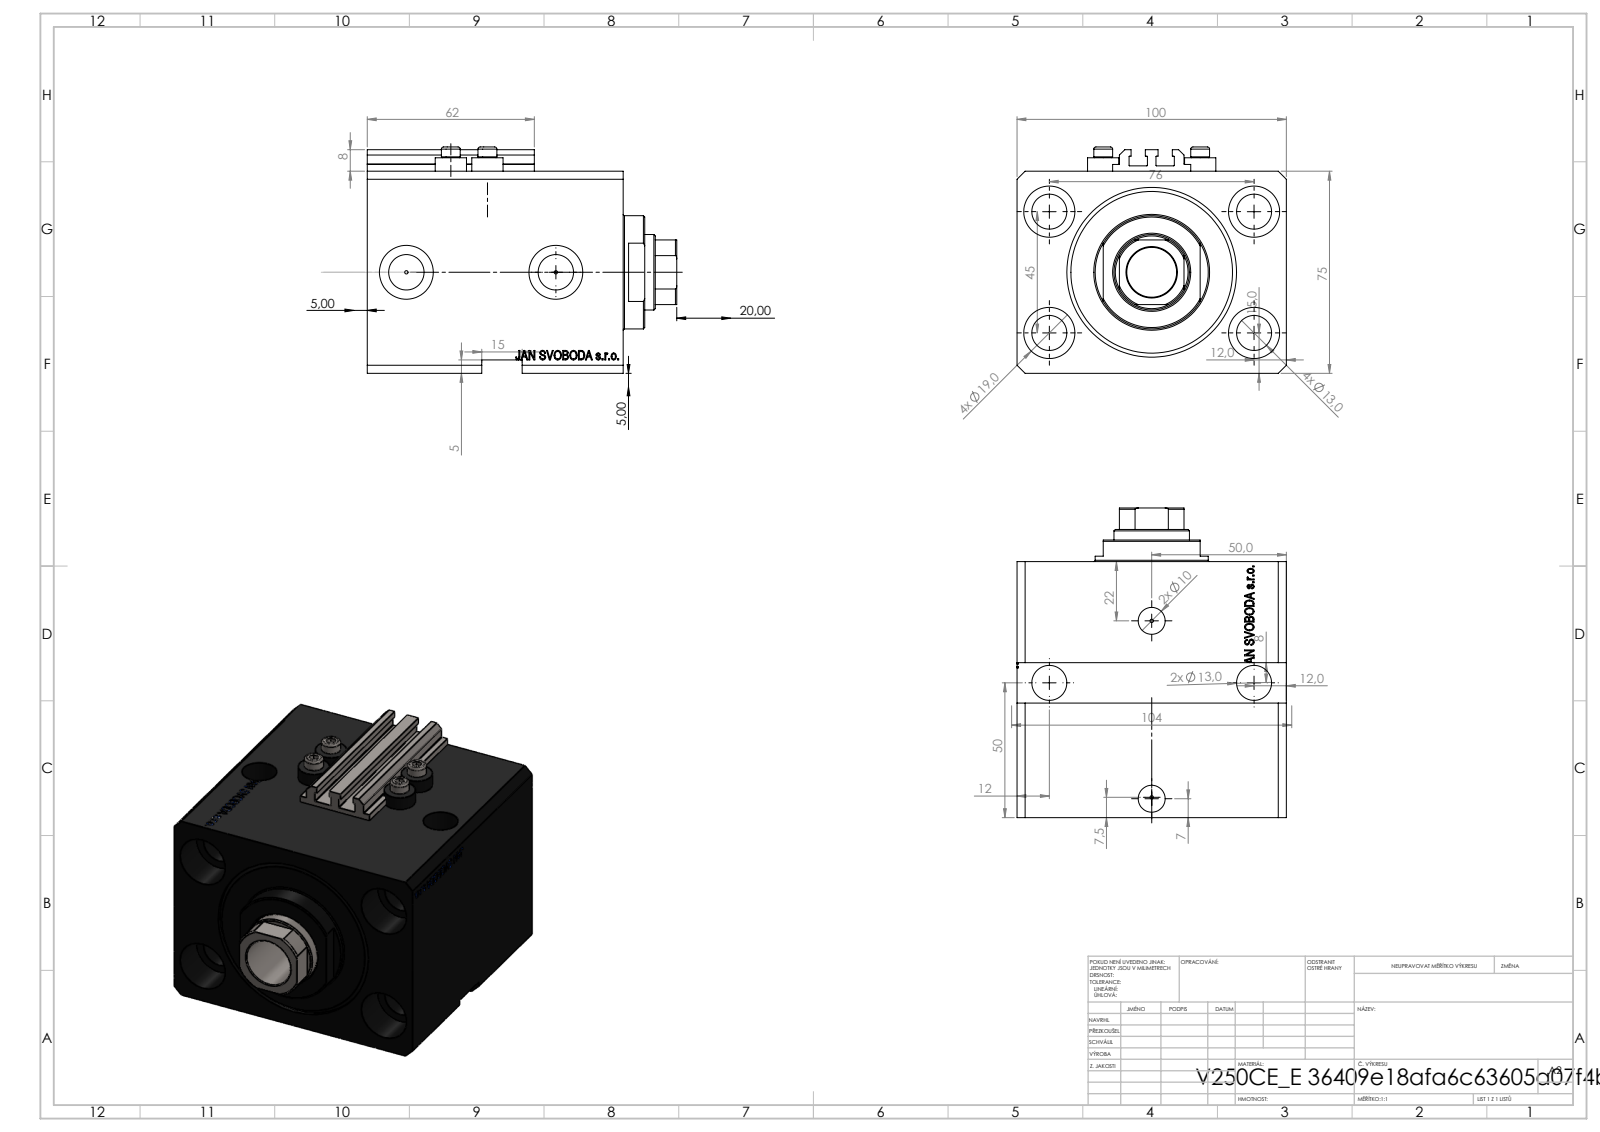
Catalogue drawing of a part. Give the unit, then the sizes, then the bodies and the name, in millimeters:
Units: millimetres
Overall size (bounding box): 114.9 × 100 × 84
Round holes (diameter × count): ⌀13 ×6, ⌀1.25 ×4, ⌀4 ×4, ⌀19 ×4, ⌀10 ×2, ⌀13.16 ×2, ⌀20 ×2, ⌀18.5 ×1, ⌀28 ×1, ⌀50 ×1, ⌀63 ×1
Round bosses / shafts (diameter × count): ⌀11.6 ×4, ⌀7 ×4, ⌀42 ×1
Partial cylindrical surfaces — rounded edges, fillets, slot ends (radius × count): R0.2 ×10, R13.5 ×1
Main face-to-face distances: 75, 100, 95, 11.9, 83.1, 68.4, 56.5, 26.6, 5, 48.4
Hole centre spacings: 44.16, 76, 13.6, 20.72, 27.59, 29.58, 30, 33.62
Volume: 610 933 mm³ · Surface area: 123 534 mm²
Bodies: 8 solids, 1088 faces (535 planar, 126 cylindrical, 427 other)
Part name (STEP PRODUCT): V250CE_C_VCP; V250CE_VC_E; ALLEN BOLT V250CE; V250CE_E_Body
STEP written by: SolidWorks 2019 (CONFIG_CONTROL_DESIGN)
